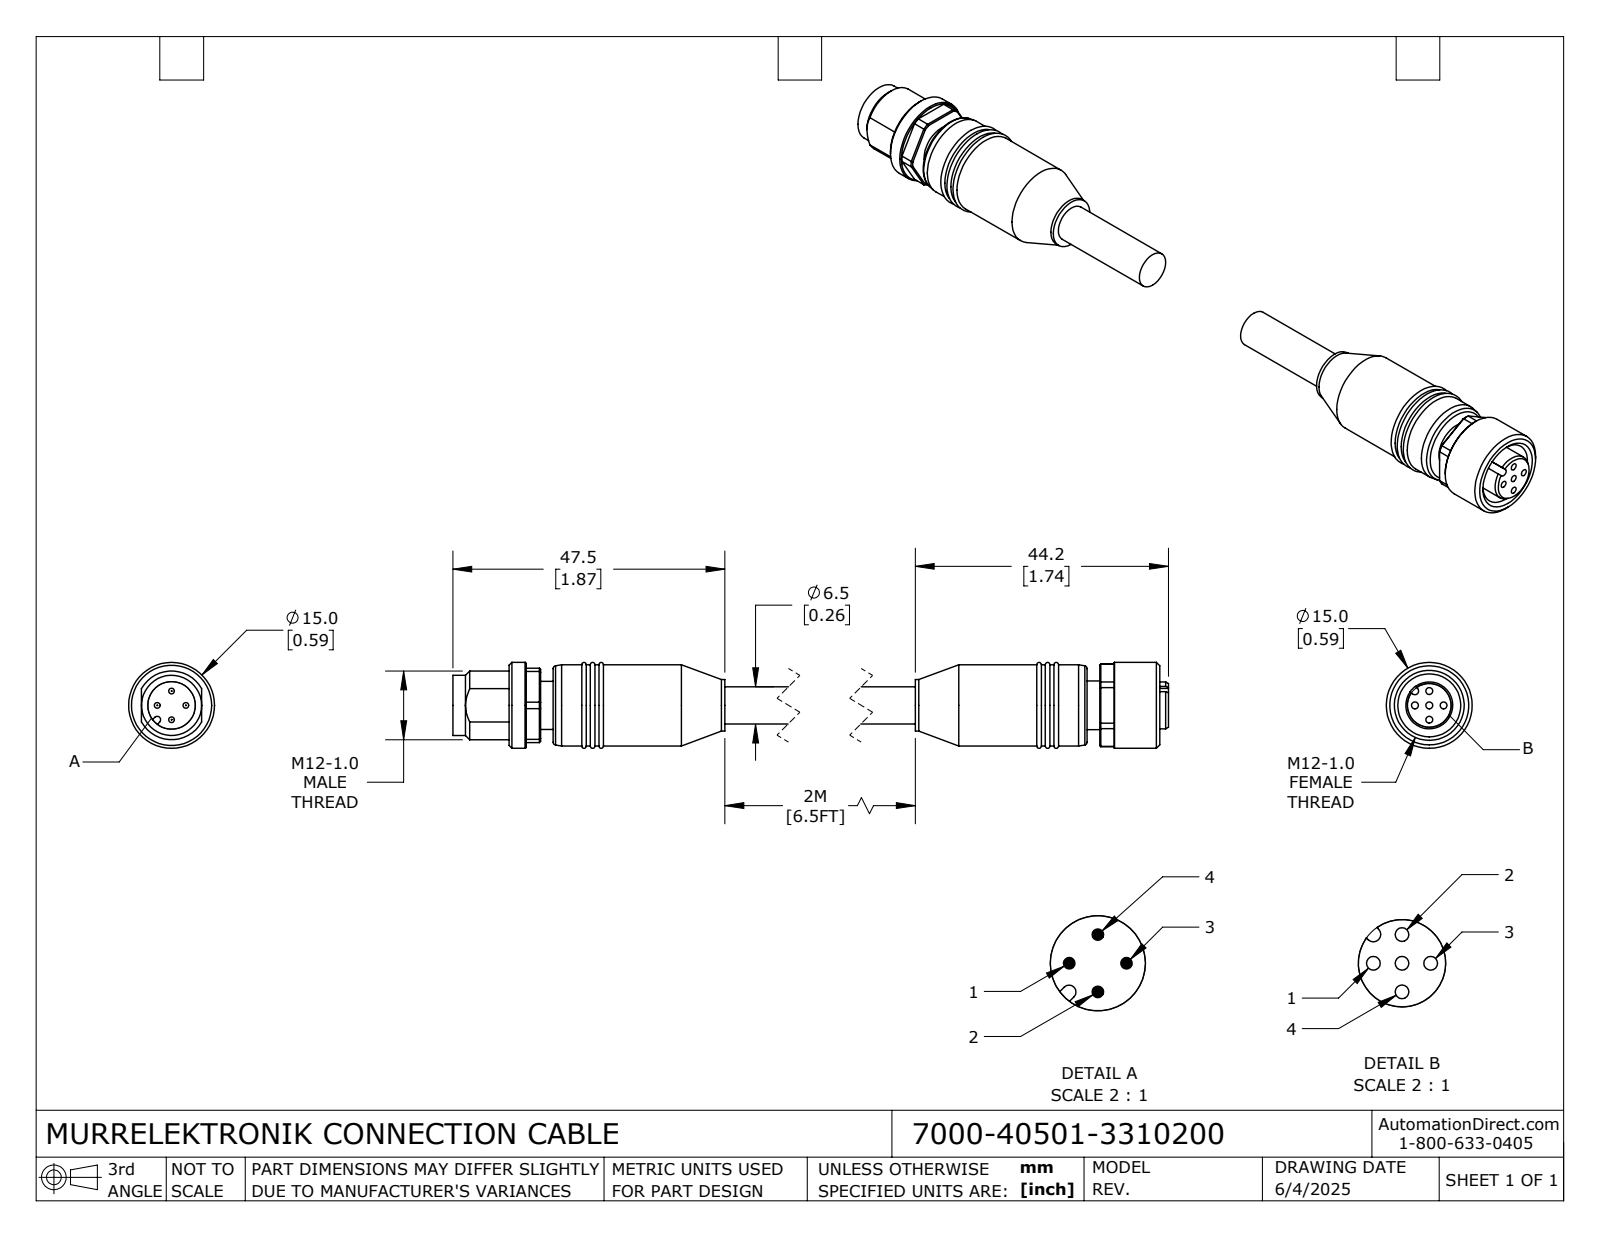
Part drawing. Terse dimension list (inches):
name: 7000-40501-3310200_MALE; 7000-40501-3310200; 7000-40501-3310200_FEMALE
written by: SolidWorks 2024 (CONFIG_CONTROL_DESIGN)
unit: in
bodies: 2 solids, 193 faces (57 planar, 75 cylindrical, 61 other)
size: 6.169 × 0.591 × 0.591
volume: 0.806 in³; area: 10.1 in²
holes: 5× ⌀0.047, 1× ⌀0.327, 1× ⌀0.433
bosses: 4× ⌀0.039, 1× ⌀0.591, 1× ⌀0.559, 1× ⌀0.413, 1× ⌀0.354, 1× ⌀0.335, 1× ⌀0.331, 1× ⌀0.323
rounds: 1× R0.024, 1× R0.026, 1× R0.236, 1× R0.283
face distances: 0.087, 5.008, 0.512, 5.094, 0.413, 4.921, 5.311, 2.055, 3.039, 1.969
hole spacings: 0.098, 0.139, 0.197
